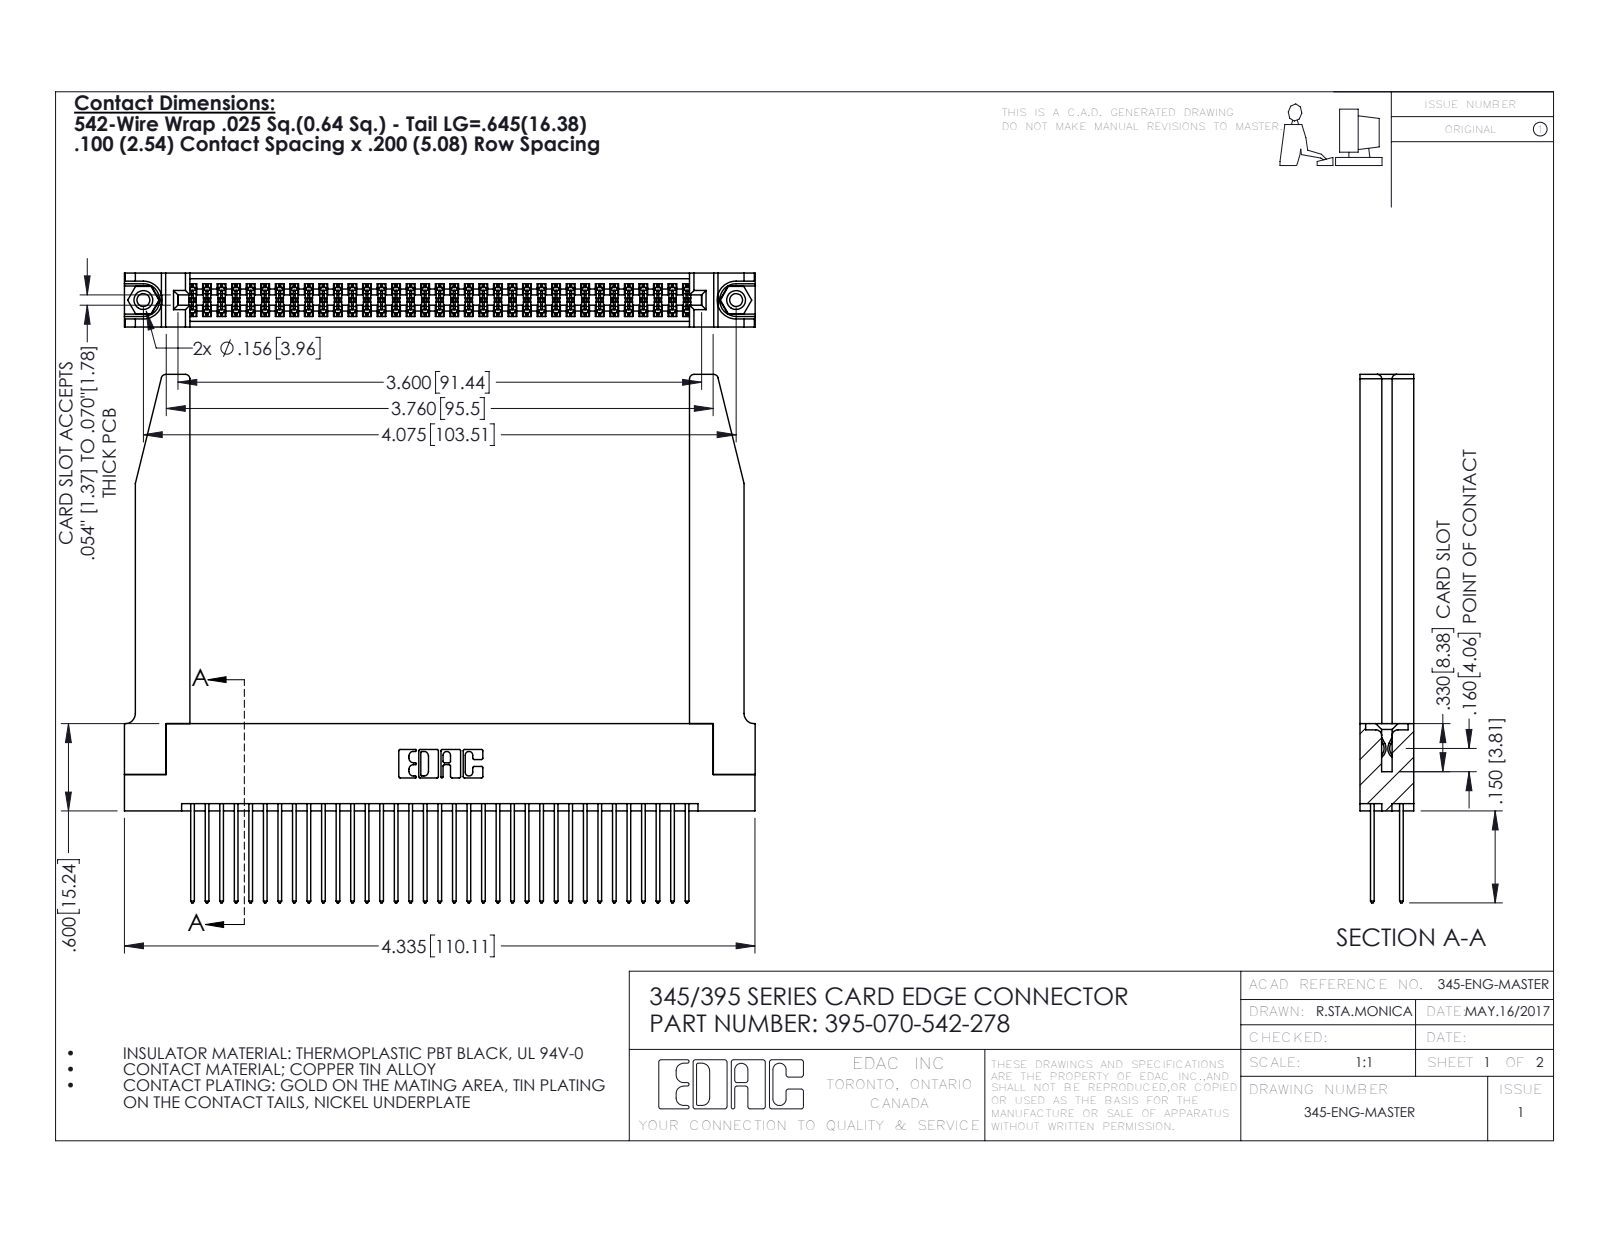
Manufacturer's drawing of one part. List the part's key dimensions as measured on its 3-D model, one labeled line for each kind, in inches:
Part name (STEP PRODUCT): 345-250-001_345-250-001-102; 345 Part_Flush Mounting Lugs - 0.156 Dia-TH; 395-070-542-278; 345-292-001_345-293-142 (+1 more)
STEP written by: SolidWorks 2016 (CONFIG_CONTROL_DESIGN)
Units: inches
Bodies: 75 solids, 3860 faces (2532 planar, 1276 cylindrical, 52 other)
Overall size (bounding box): 4.336 × 3.632 × 0.37
Volume: 1.143 in³ · Surface area: 37.86 in²
Round holes (diameter × count): ⌀0.089 ×2, ⌀0.125 ×2, ⌀0.156 ×2, ⌀0.064 ×1
Round bosses / shafts (diameter × count): ⌀0.155 ×2
Partial cylindrical surfaces — rounded edges, fillets, slot ends (radius × count): R0.006 ×105, R0.01 ×70, R0.01 ×22, R0.03 ×8, R0.007 ×6, R0.031 ×6, R0.026 ×3, R0.014 ×2
Main face-to-face distances: 0.072, 0.298, 0.37, 0.2, 0.098, 0.272, 0.025, 0.225, 0.175, 0.148
Hole centre spacings: 0.27, 3.839, 4.075
